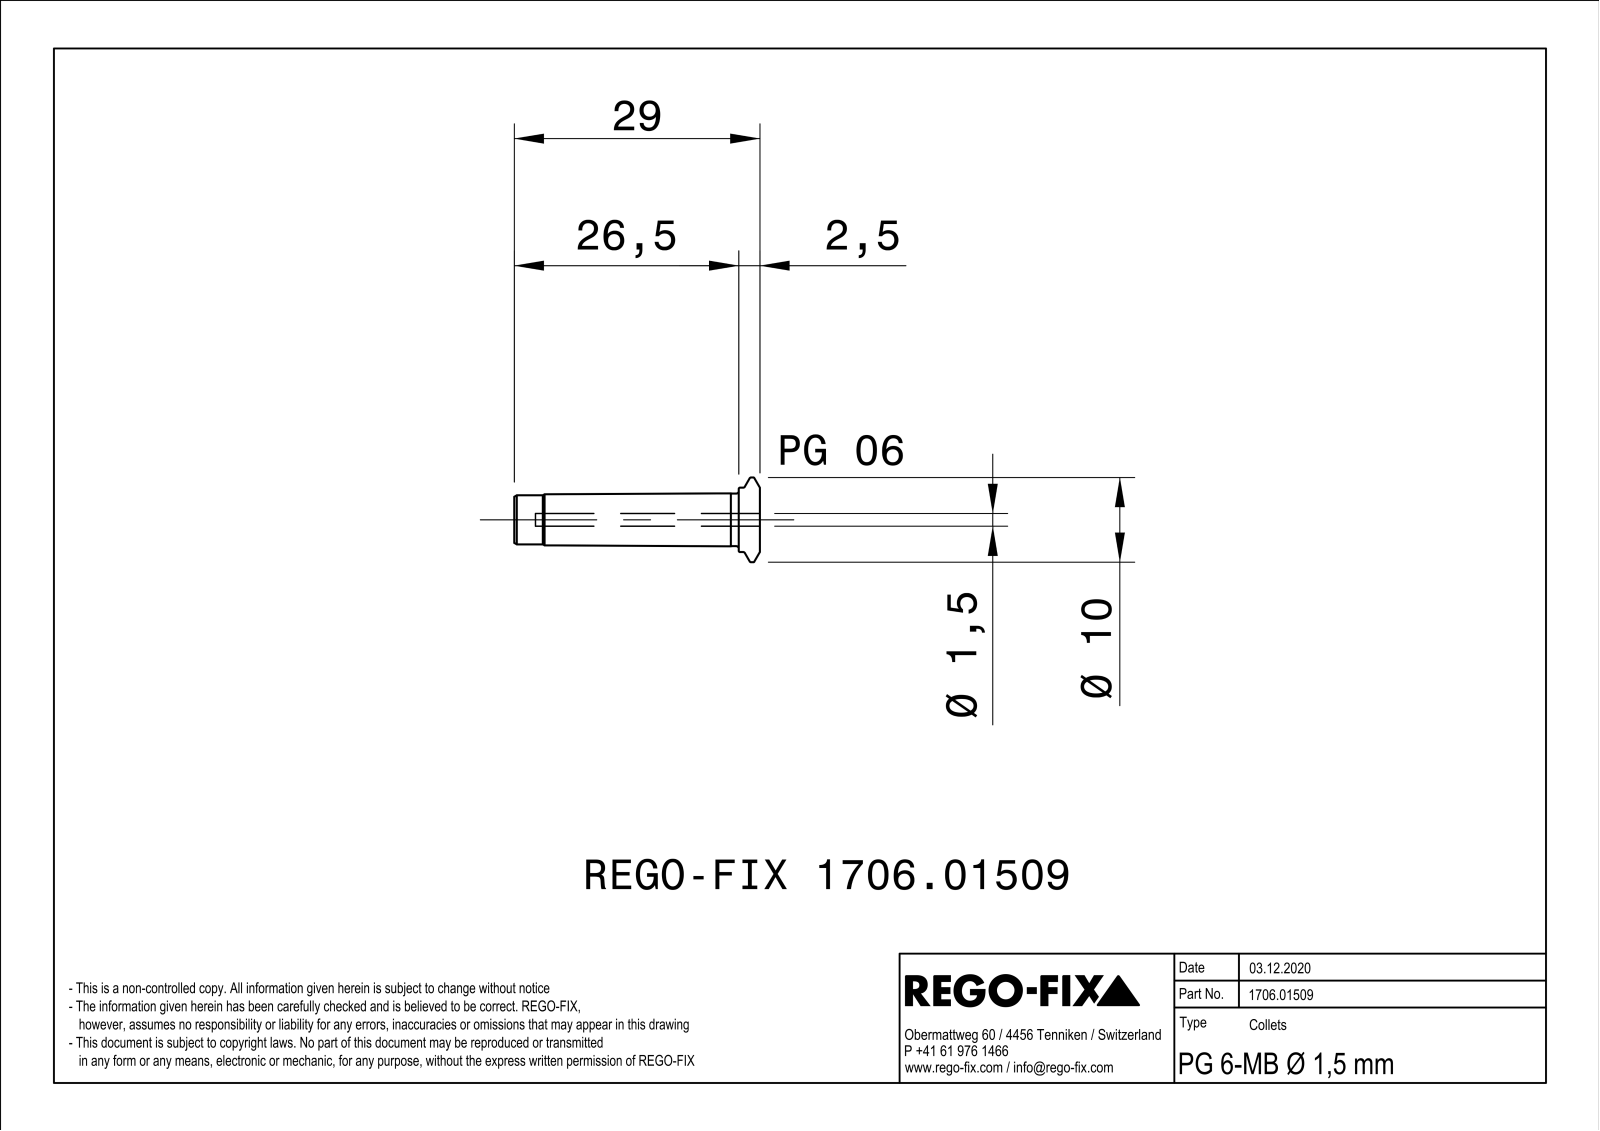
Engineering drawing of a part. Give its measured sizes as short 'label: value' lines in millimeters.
name: NOCUT
written by: SIEMENS PLM Software Solid Edge ST10 (AUTOMOTIVE_DESIGN)
unit: mm
bodies: 1 solid, 75 faces (18 planar, 17 cylindrical, 40 other)
size: 29 × 10 × 9.99
volume: 611 mm³; area: 1 404 mm²
holes: 4× ⌀1.5
bosses: 1× ⌀10, 1× ⌀7.6, 1× ⌀6.2, 1× ⌀5.8
rounds: 1× R1.73
face distances: 0.45, 0.46, 29, 20, 9, 2.5, 17.5, 26.5
hole spacings: 3.22, 1.92, 1.75
